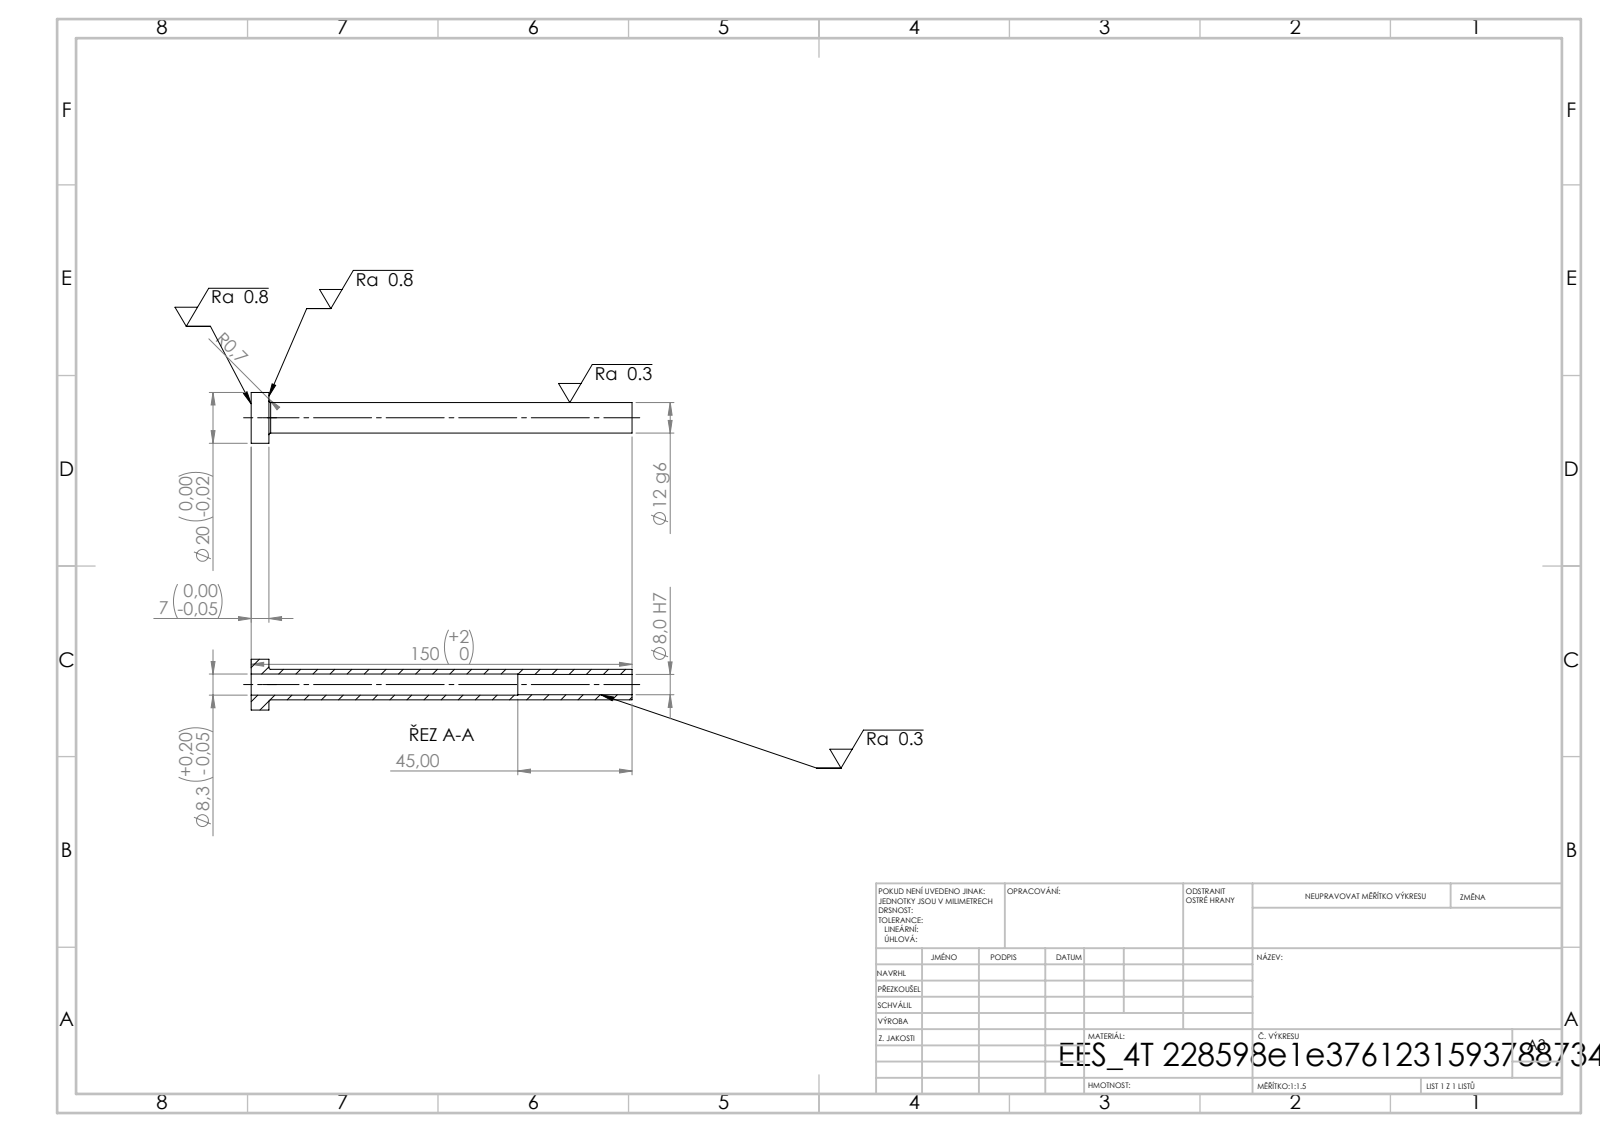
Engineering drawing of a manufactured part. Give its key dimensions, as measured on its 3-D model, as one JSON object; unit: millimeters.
{"step_written_by": "SolidWorks 2019 (CONFIG_CONTROL_DESIGN)", "units": "millimeters", "bodies": {"solids": 1, "faces": 14, "planar": 4, "cylindrical": 8, "other": 2}, "overall_size": [150, 20, 20], "volume_mm3": 10433, "surface_area_mm2": 10216, "round_holes": [[8, 1], [8.3, 1]], "round_bosses_or_shafts": [[20, 1], [12, 1]], "face_to_face_distances": [7, 150, 143, 105, 98, 45]}
